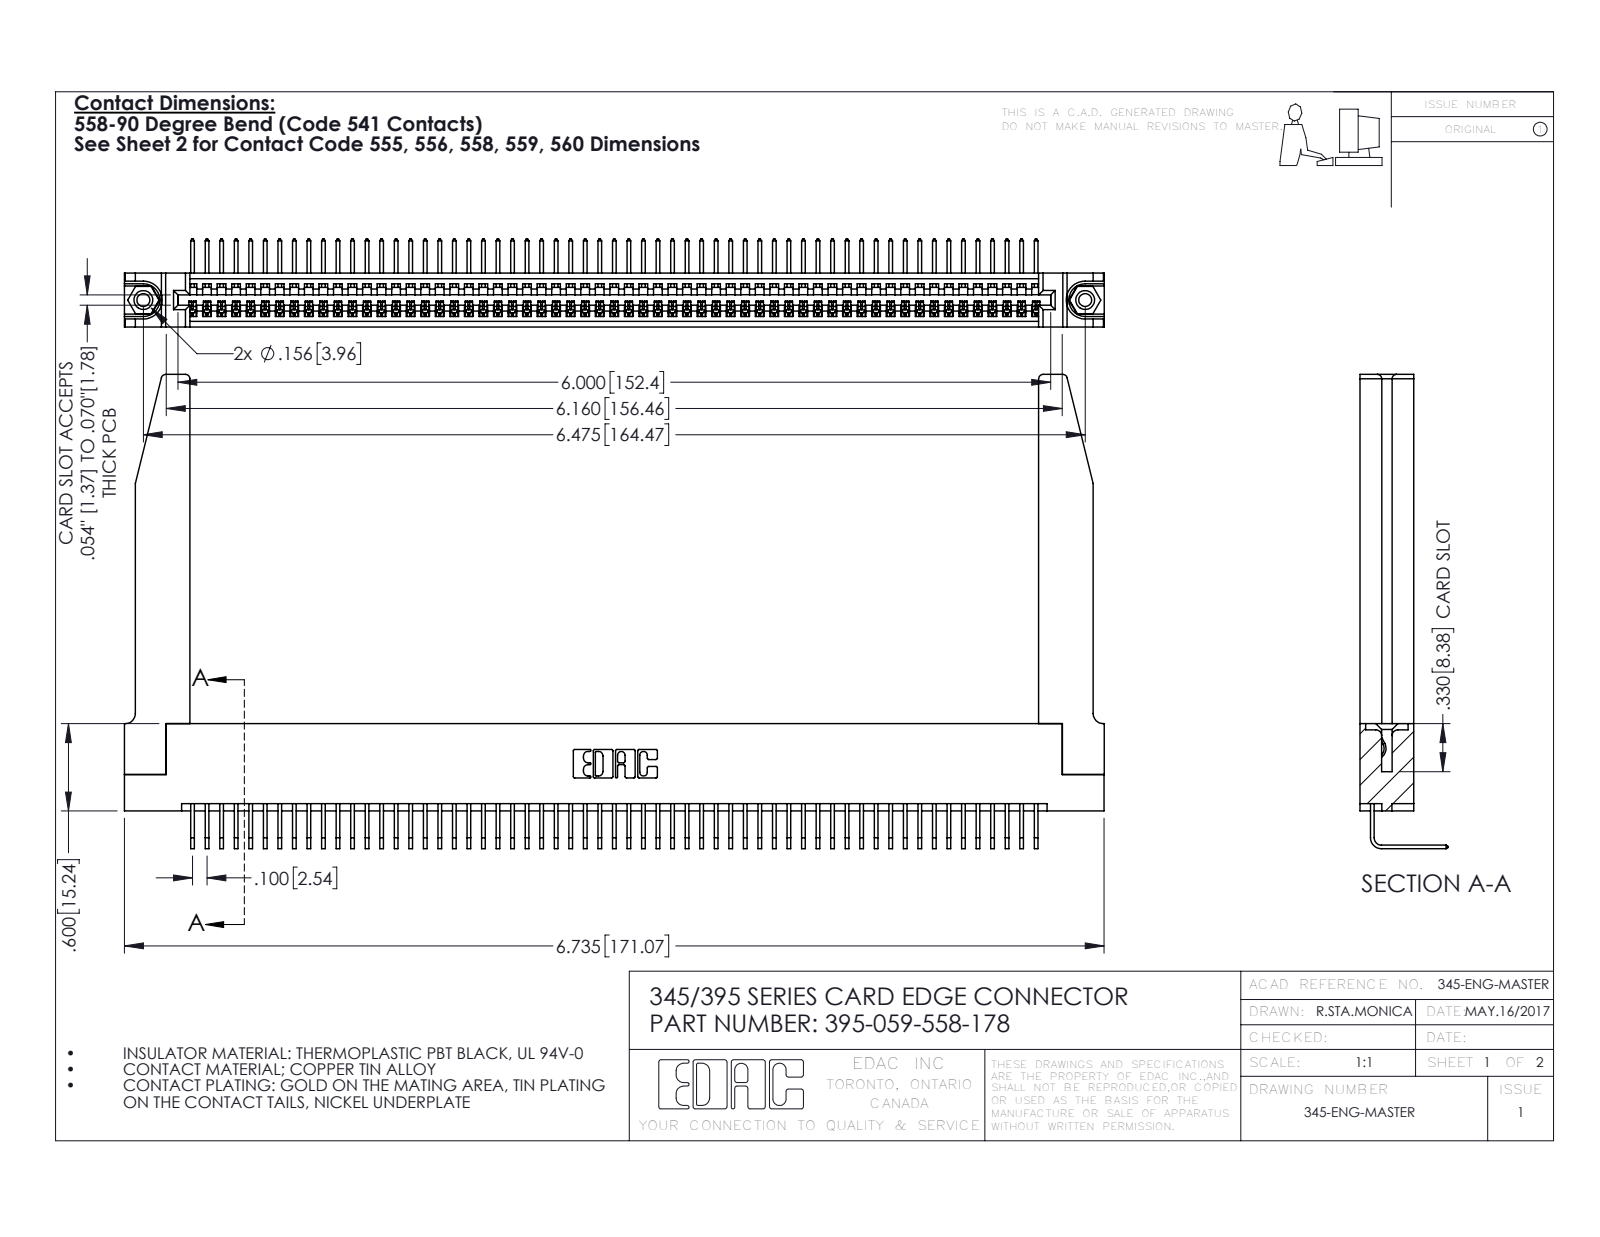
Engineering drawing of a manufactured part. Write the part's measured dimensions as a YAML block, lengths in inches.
part_name: "345 Part_Flush Mounting Lugs - 0.156 Dia-TH; 345-292-001_558 Tail - 2; 395-059-558-178; 345-250-001_345-250-001-102 (+1 more)"
step_written_by: "SolidWorks 2016 (CONFIG_CONTROL_DESIGN)"
units: inches
bodies: {solids: 64, faces: 3900, planar: 2700, cylindrical: 1148, other: 52}
overall_size: [6.736, 3.259, 0.605]
volume: 1.486
surface_area: 46.92
round_holes:
  - {diameter: 0.089, count: 2}
  - {diameter: 0.125, count: 2}
  - {diameter: 0.156, count: 2}
  - {diameter: 0.064, count: 1}
round_bosses_or_shafts:
  - {diameter: 0.155, count: 2}
partial_cylinders:
  - {radius: 0.006, count: 118}
  - {radius: 0.01, count: 22}
  - {radius: 0.03, count: 8}
  - {radius: 0.007, count: 6}
  - {radius: 0.031, count: 6}
  - {radius: 0.026, count: 3}
  - {radius: 0.031, count: 2}
  - {radius: 0.04, count: 2}
face_to_face_distances: [0.072, 0.37, 0.298, 0.2, 0.098, 0.272, 0.025, 0.225, 0.148, 0.15]
hole_center_spacings: [0.27, 6.239, 6.475]
